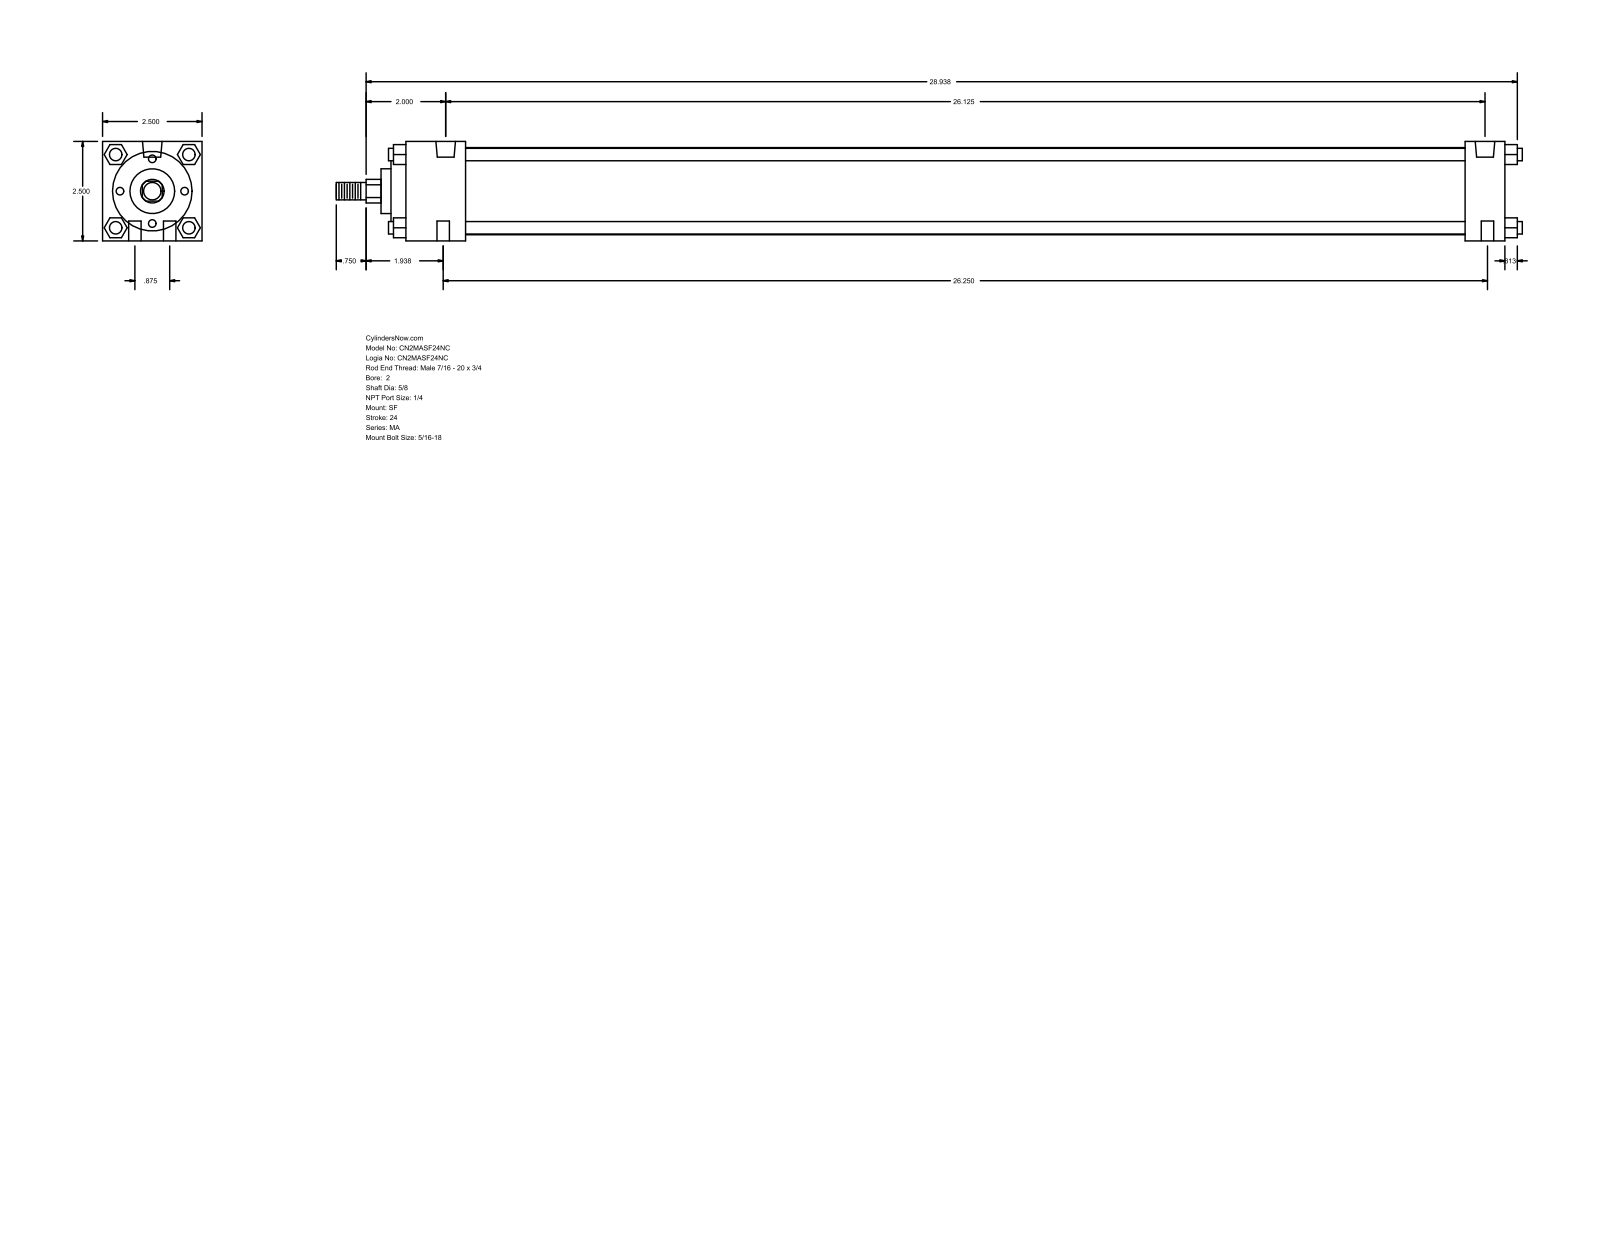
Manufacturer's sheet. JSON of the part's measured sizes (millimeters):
{"part_name": "MA_SF__0200_0.625", "step_written_by": "GSSL Pune (CONFIG_CONTROL_DESIGN)", "units": "millimeters", "bodies": {"solids": 0, "faces": 126, "planar": 95, "cylindrical": 31, "other": 0}, "overall_size": [757.24, 63.5, 63.5], "round_holes": [[7.94, 6], [12.49, 2]], "round_bosses_or_shafts": [[7.94, 4], [55.63, 1], [50.8, 1], [28.57, 1], [15.88, 1], [11.11, 1]], "partial_cylinders_radius": [[7.54, 1]], "face_to_face_distances": [63.5, 12.7, 38.1, 701.68, 676.27, 25.41, 638.17, 663.58, 9.52, 47.62], "hole_center_spacings": [11.22, 22.22, 663.58, 665.25, 665.26, 666.75, 667.12]}
